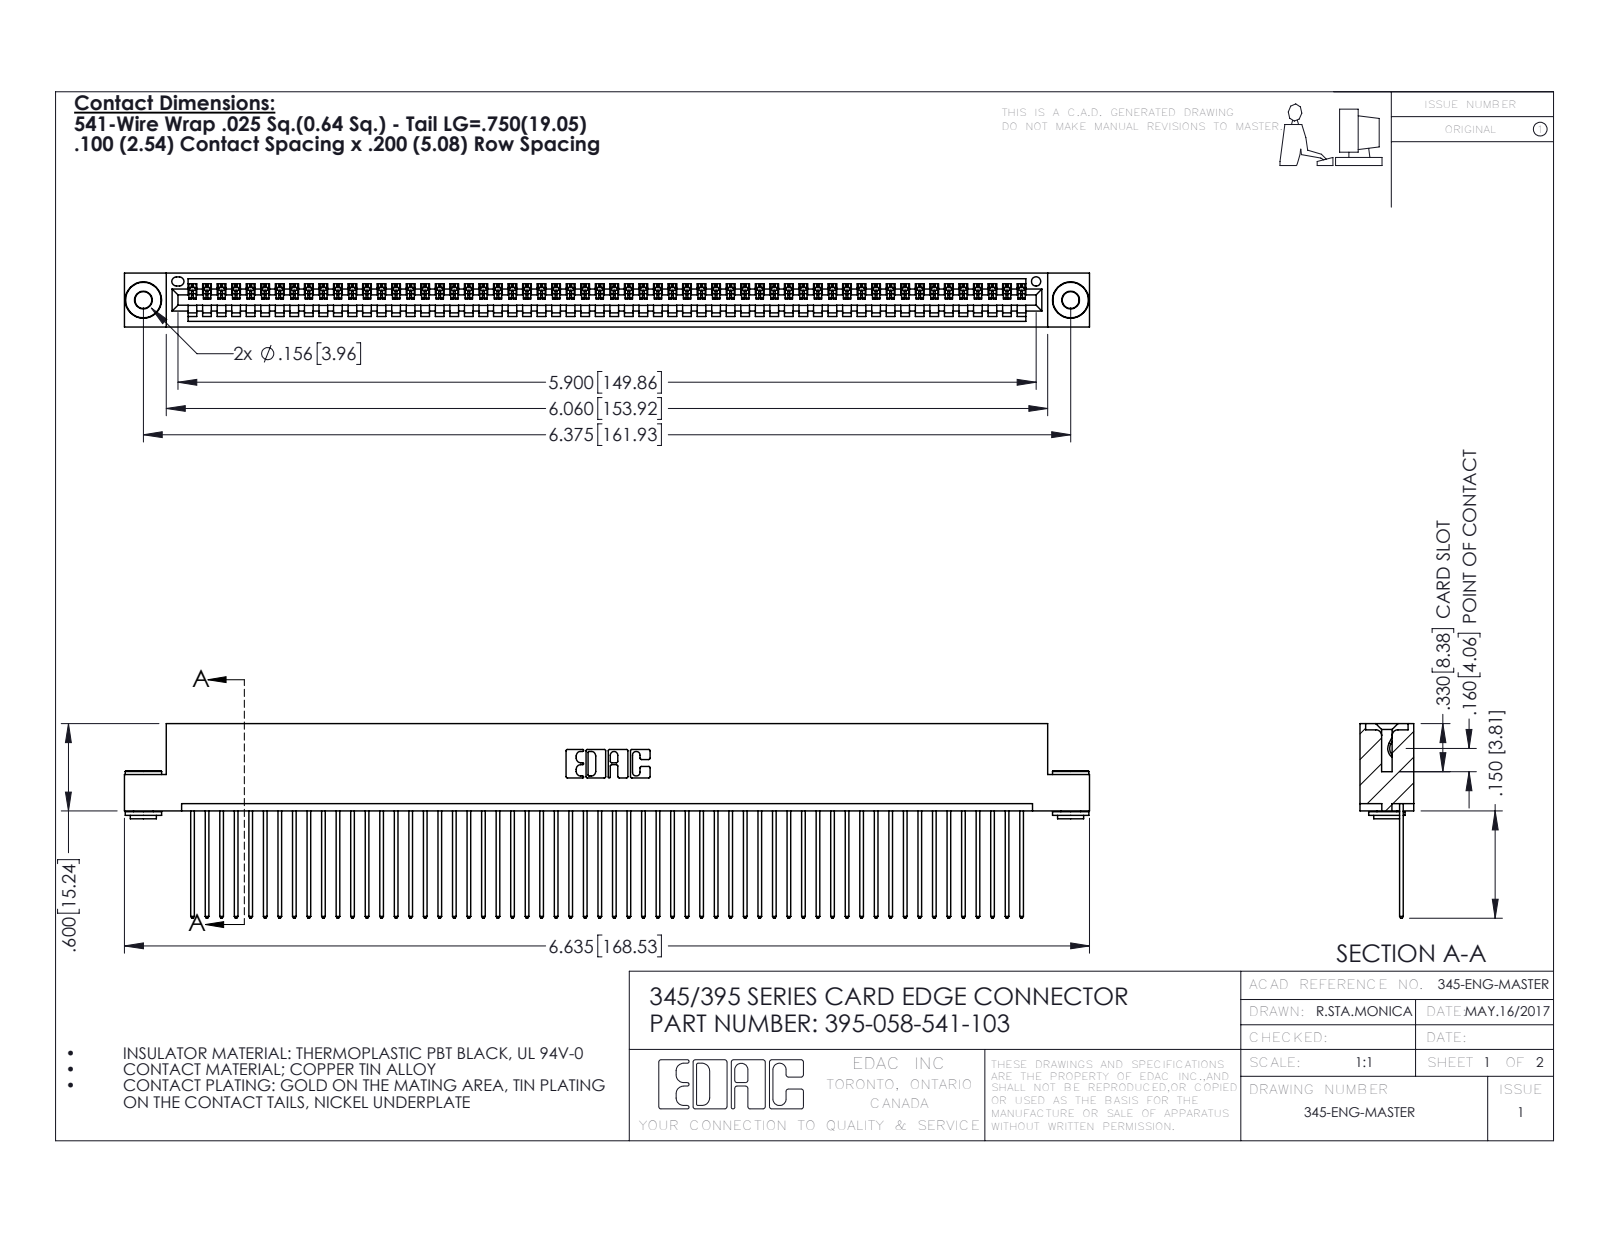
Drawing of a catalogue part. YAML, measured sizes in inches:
part_name: "345-250-002_345-250-002-102; 345-292-001_345-293-141; 395-058-541-103; 345 Part_Flush Mounting Lugs - 0.156 Dia-TH"
step_written_by: "SolidWorks 2016 (CONFIG_CONTROL_DESIGN)"
units: inches
bodies: {solids: 61, faces: 3528, planar: 2410, cylindrical: 1110, other: 8}
overall_size: [6.635, 1.337, 0.37]
volume: 0.998
surface_area: 36.09
round_holes:
  - {diameter: 0.116, count: 2}
  - {diameter: 0.156, count: 2}
  - {diameter: 0.064, count: 1}
round_bosses_or_shafts:
  - {diameter: 0.25, count: 2}
  - {diameter: 0.18, count: 2}
  - {diameter: 0.136, count: 2}
partial_cylinders:
  - {radius: 0.006, count: 116}
  - {radius: 0.01, count: 116}
  - {radius: 0.01, count: 22}
  - {radius: 0.007, count: 6}
  - {radius: 0.031, count: 6}
  - {radius: 0.026, count: 3}
  - {radius: 0.031, count: 2}
  - {radius: 0.04, count: 2}
face_to_face_distances: [0.072, 0.298, 0.025, 0.098, 0.272, 0.37, 0.2, 0.225, 0.149, 0.072]
hole_center_spacings: [0.27, 6.139, 6.375]
